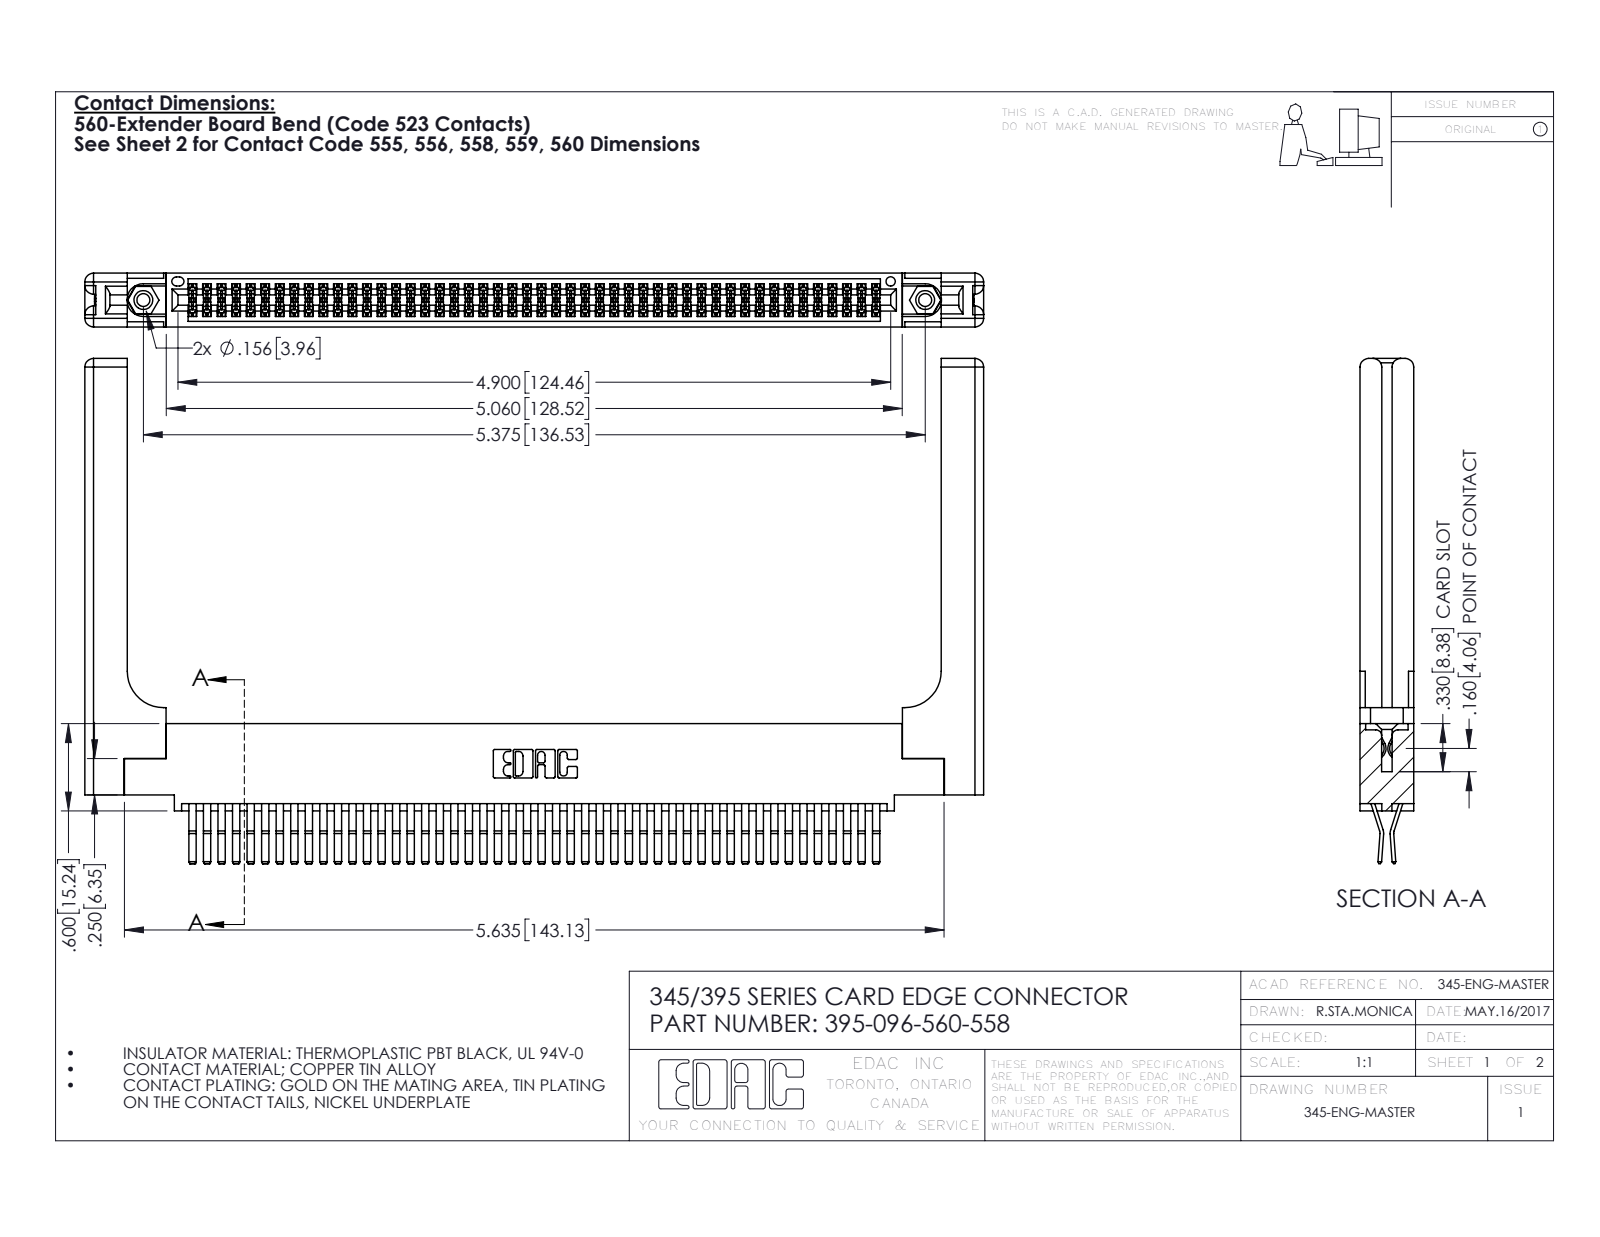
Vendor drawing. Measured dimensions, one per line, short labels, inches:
name: 345-220-058_345-220-058; 345-250-001_345-250-001-102; 345 Part_0.110 Offset - 0.156 Dia-TH; 395-096-560-558 (+1 more)
written by: SolidWorks 2016 (CONFIG_CONTROL_DESIGN)
unit: in
bodies: 101 solids, 5378 faces (3400 planar, 1918 cylindrical, 60 other)
size: 6.179 × 3.472 × 0.37
volume: 1.485 in³; area: 47.01 in²
holes: 2× ⌀0.089, 2× ⌀0.125, 2× ⌀0.156, 1× ⌀0.064
bosses: 2× ⌀0.155
rounds: 145× R0.006, 22× R0.01, 16× R0.06, 6× R0.007, 6× R0.031, 3× R0.026, 2× R0.01, 2× R0.014
face distances: 0.072, 0.37, 0.298, 0.025, 0.098, 0.272, 0.2, 0.225, 0.148, 0.15
hole spacings: 0.27, 5.139, 5.375
